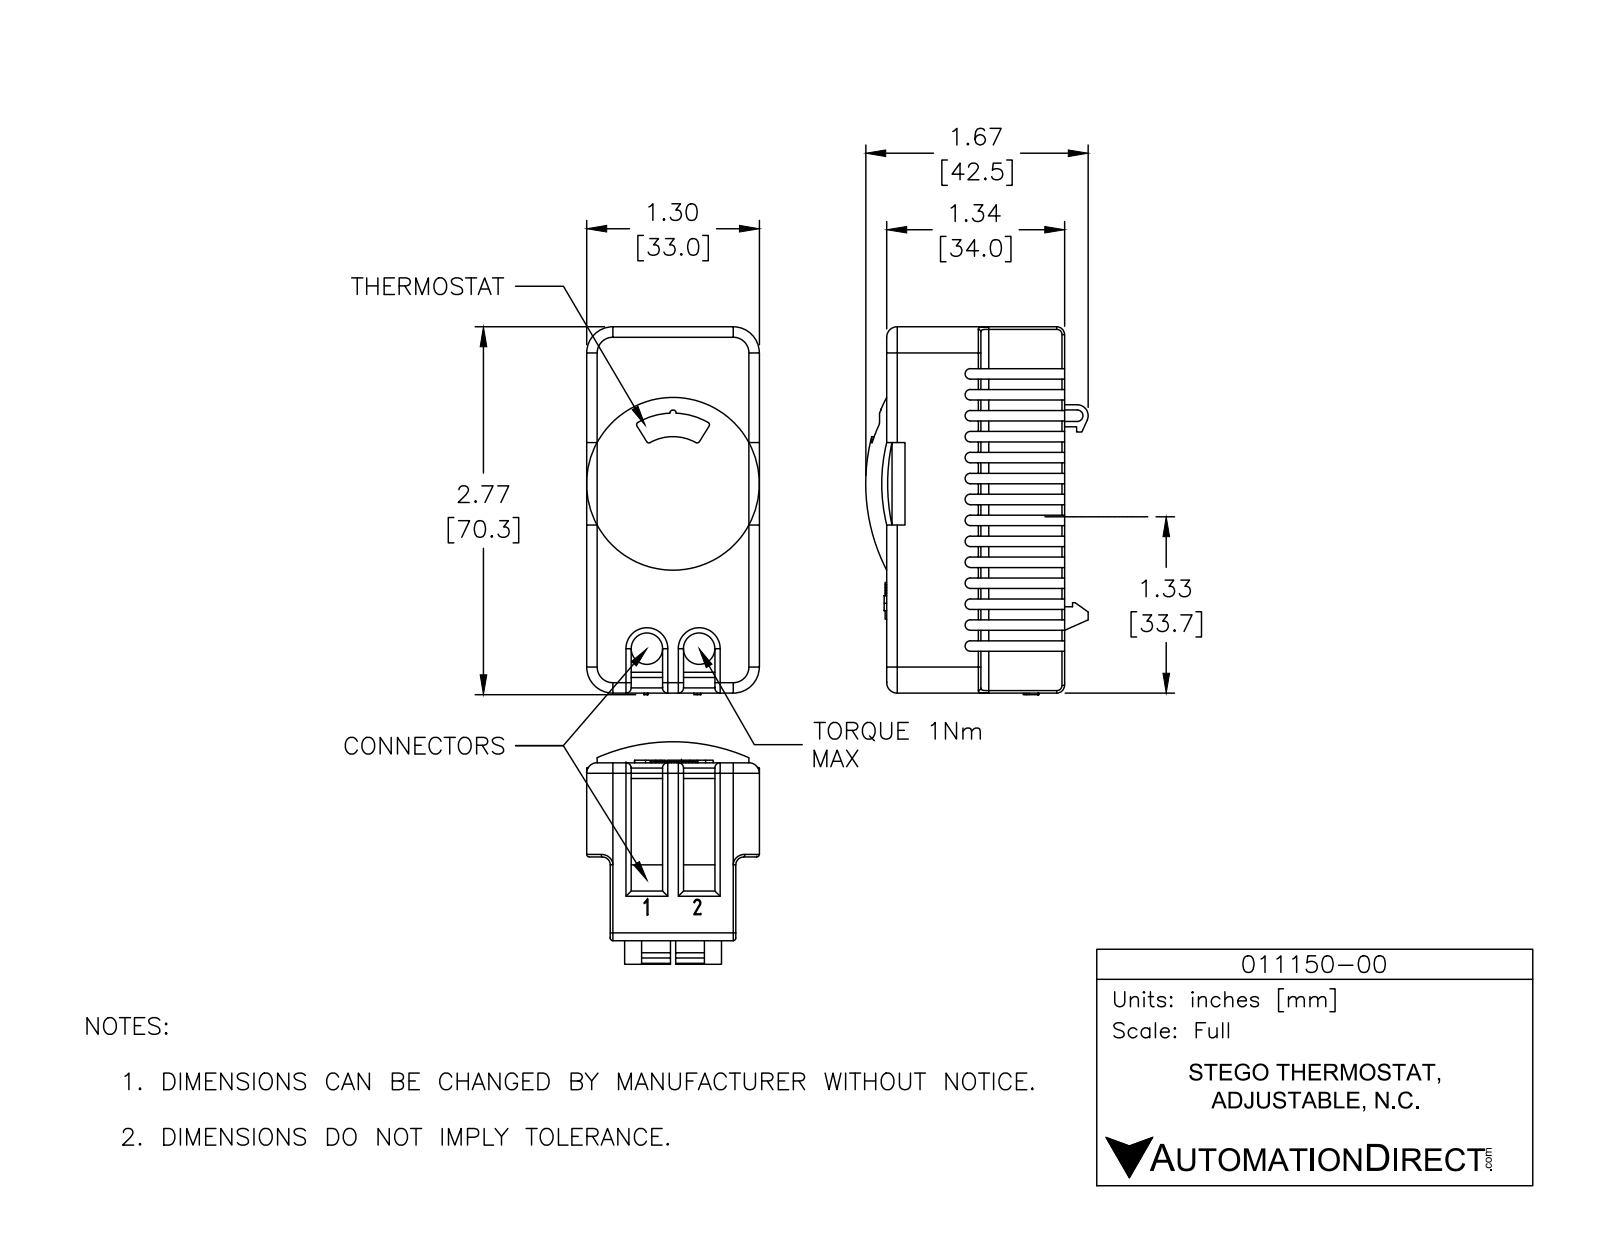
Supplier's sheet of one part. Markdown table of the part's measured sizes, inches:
| quantity | value |
| --- | --- |
| part name | STO_011_EPLAN_07_2013 |
| STEP written by | SolidWorks 2013 (AUTOMOTIVE_DESIGN) |
| units | inches |
| bodies | 1 solid, 650 faces (373 planar, 199 cylindrical, 78 other) |
| overall size | 2.768 × 1.673 × 1.299 |
| volume | 3.911 in³ |
| surface area | 24.99 in² |
| round holes (diameter × count) | 0.236 × 2 |
| partial cylindrical surfaces (radius × count) | 0.039 × 29, 0.02 × 12, 0.059 × 4, 0.079 × 4, 0.197 × 4, 0.024 × 1, 0.043 × 1, 0.083 × 1 |
| main face-to-face distances | 0.157, 0.315, 0.276, 0.63, 0.472, 0.945, 1.024, 0.177, 0.787, 1.339 |
| hole center spacings | 0.394 |
